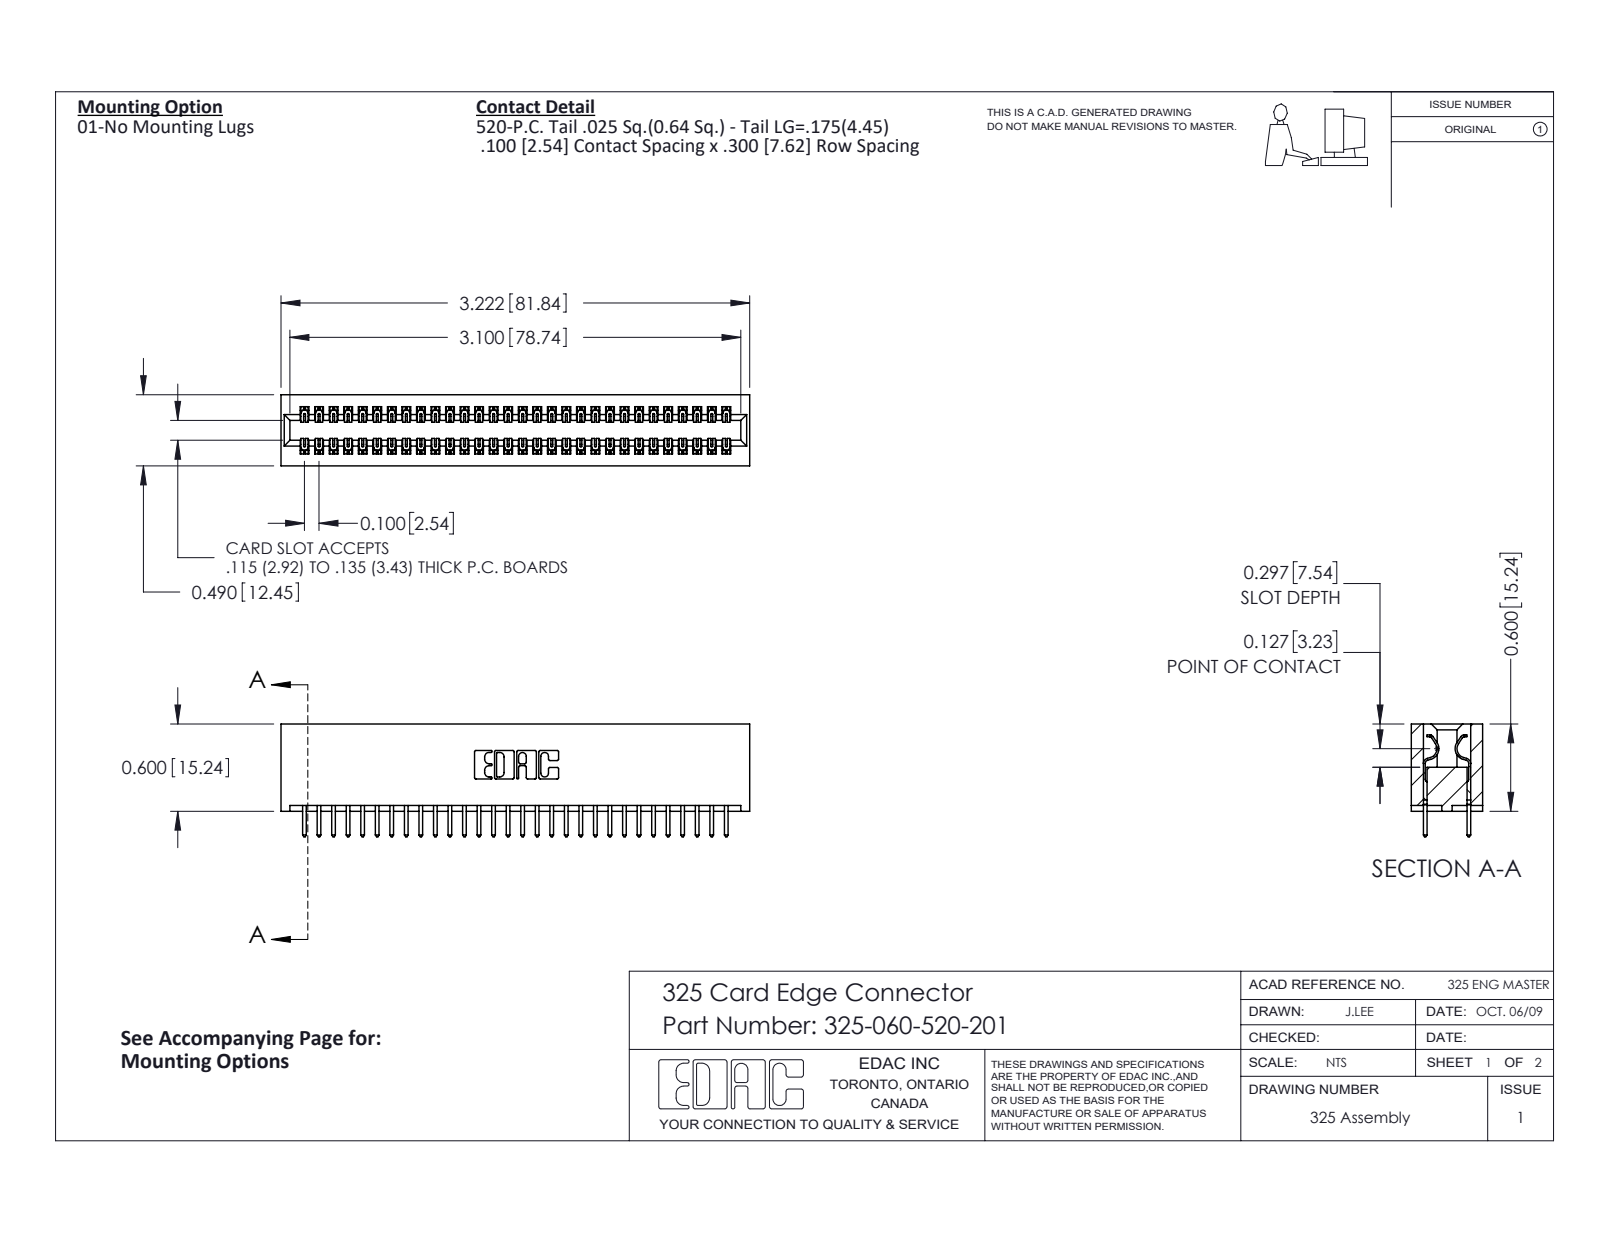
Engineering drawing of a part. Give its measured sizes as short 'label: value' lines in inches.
name: 325 Part_Lugless; 325-060-520-201; 325-292-001_325-293-120
written by: SolidWorks 2016 (CONFIG_CONTROL_DESIGN)
unit: in
bodies: 61 solids, 3226 faces (2226 planar, 1000 cylindrical, 0 other)
size: 3.222 × 0.775 × 0.49
volume: 0.675 in³; area: 21.13 in²
rounds: 90× R0.006, 60× R0.01, 22× R0.01, 6× R0.007, 6× R0.031, 3× R0.026, 2× R0.014, 2× R0.022
face distances: 0.083, 0.407, 0.3, 0.49, 0.107, 0.383, 0.025, 0.325, 0.275, 0.1
